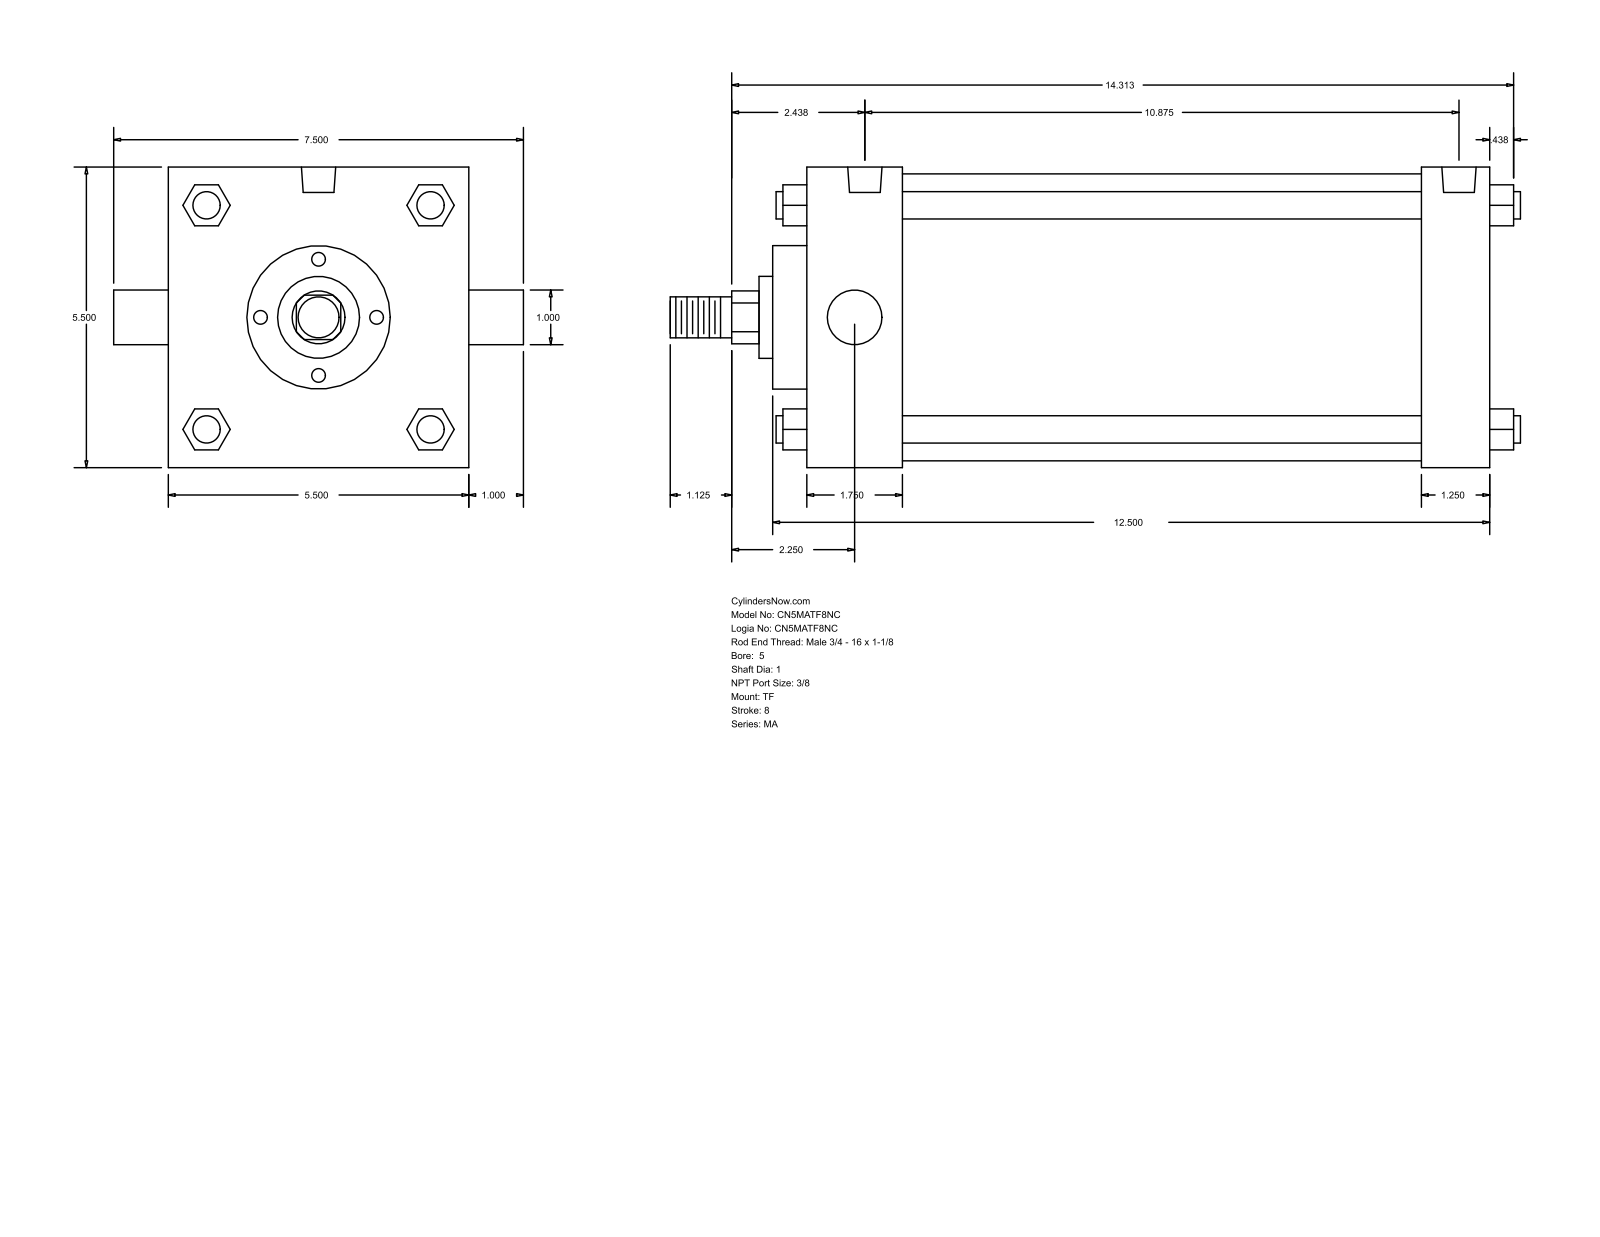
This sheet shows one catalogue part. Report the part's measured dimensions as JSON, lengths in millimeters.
{"part_name": "MA_TF__0500_1", "step_written_by": "GSSL Pune (CONFIG_CONTROL_DESIGN)", "units": "millimeters", "bodies": {"solids": 0, "faces": 122, "planar": 93, "cylindrical": 29, "other": 0}, "overall_size": [395.29, 190.5, 139.7], "round_holes": [[11.11, 3], [15.93, 2]], "round_bosses_or_shafts": [[12.7, 4], [25.4, 2], [133.35, 1], [66.67, 1], [38.1, 1], [19.05, 1]], "partial_cylinders_radius": [[12.29, 1]], "face_to_face_distances": [139.7, 317.51, 285.76, 31.75, 44.46, 241.3, 273.05, 15.87, 60.33, 301.63], "hole_center_spacings": [4.76, 271.47, 266.71, 276.23]}
